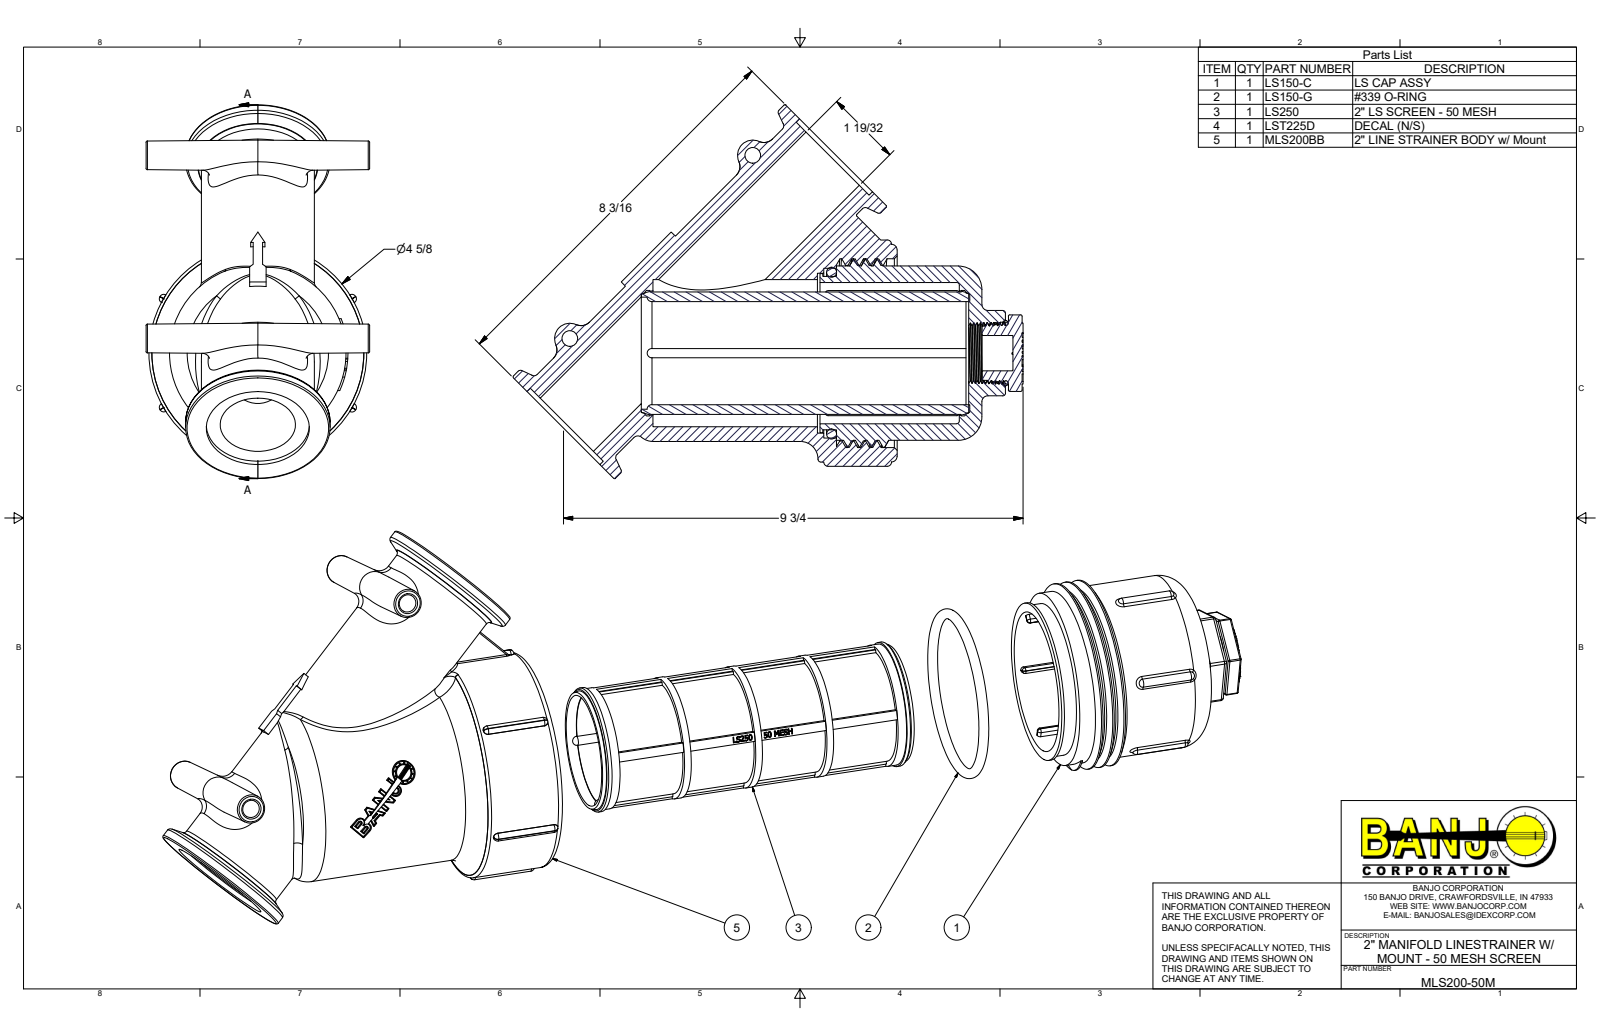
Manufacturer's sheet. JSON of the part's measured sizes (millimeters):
{"part_name": "MLS200BB; LS150XC; LSQ200-PL; LSQ200-R (+4 more)", "step_written_by": "Autodesk Inventor 2014 (AUTOMOTIVE_DESIGN)", "units": "millimeters", "bodies": {"solids": 5, "faces": 1347, "planar": 659, "cylindrical": 251, "other": 437}, "overall_size": [275.29, 201.6, 120.65], "volume_mm3": 959838, "surface_area_mm2": 325703, "round_holes": [[55.63, 3], [40.64, 2], [8.36, 1], [11.81, 1], [19.05, 1], [29.87, 1], [59.69, 1], [76.2, 1], [79.38, 1], [86.23, 1], [91.57, 1], [94.73, 1]], "round_bosses_or_shafts": [[77.98, 2], [117.47, 1], [95.25, 1], [94.04, 1], [85.85, 1], [82.73, 1], [67.72, 1], [66.04, 1]], "partial_cylinders_radius": [[1.52, 46], [2.29, 35], [0.76, 24], [2.38, 6], [3.17, 6], [2.54, 4], [0.72, 2], [1.04, 2]], "face_to_face_distances": [71.37, 2.54, 205.45, 207.99, 36.7, 5.08, 105.39, 176.76, 40.51, 81.03]}
